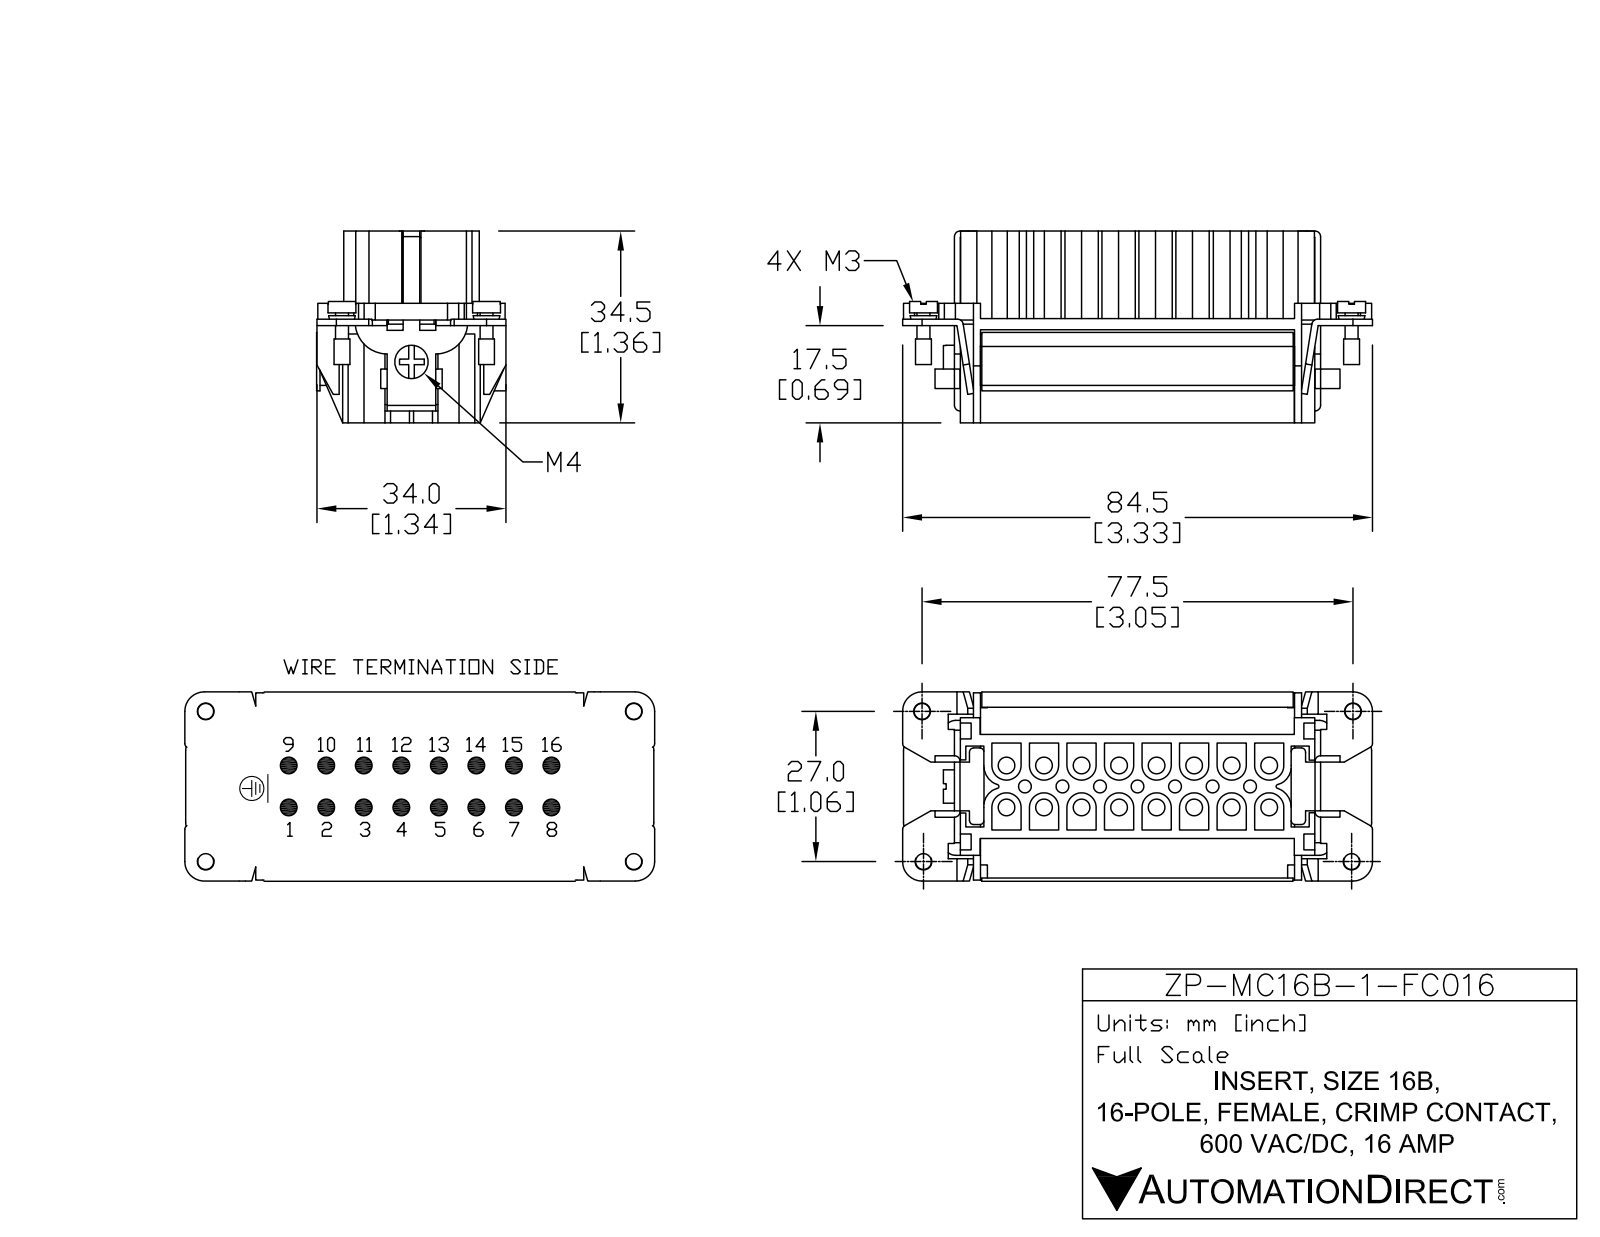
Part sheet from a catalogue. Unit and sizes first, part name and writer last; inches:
Units: inches
Overall size (bounding box): 3.346 × 1.398 × 1.362
Round holes (diameter × count): ⌀0.226 ×16, ⌀0.015 ×7, ⌀0.071 ×7, ⌀0.106 ×4
Round bosses / shafts (diameter × count): ⌀0.016 ×5, ⌀0.213 ×4, ⌀0.205 ×4, ⌀0.118 ×4, ⌀0.091 ×4, ⌀0.015 ×4, ⌀0.276 ×1, ⌀0.197 ×1
Partial cylindrical surfaces — rounded edges, fillets, slot ends (radius × count): R0.02 ×40, R0.008 ×36, R0.012 ×28, R0.039 ×20, R0.112 ×16, R0.047 ×10, R0.079 ×10, R0.059 ×8
Main face-to-face distances: 0.264, 0.791, 0.059, 0.047, 0.528, 1.287, 0.321, 0.016, 1.041, 0.982
Hole centre spacings: 0.198, 0.422, 0.264, 0.676, 0.528, 0.935, 0.396, 0.791
Bodies: 3 solids, 2386 faces (1519 planar, 453 cylindrical, 414 other)
Part name (STEP PRODUCT): ZP-MC16B-1-FC016
STEP written by: SolidWorks 2021 (CONFIG_CONTROL_DESIGN)
